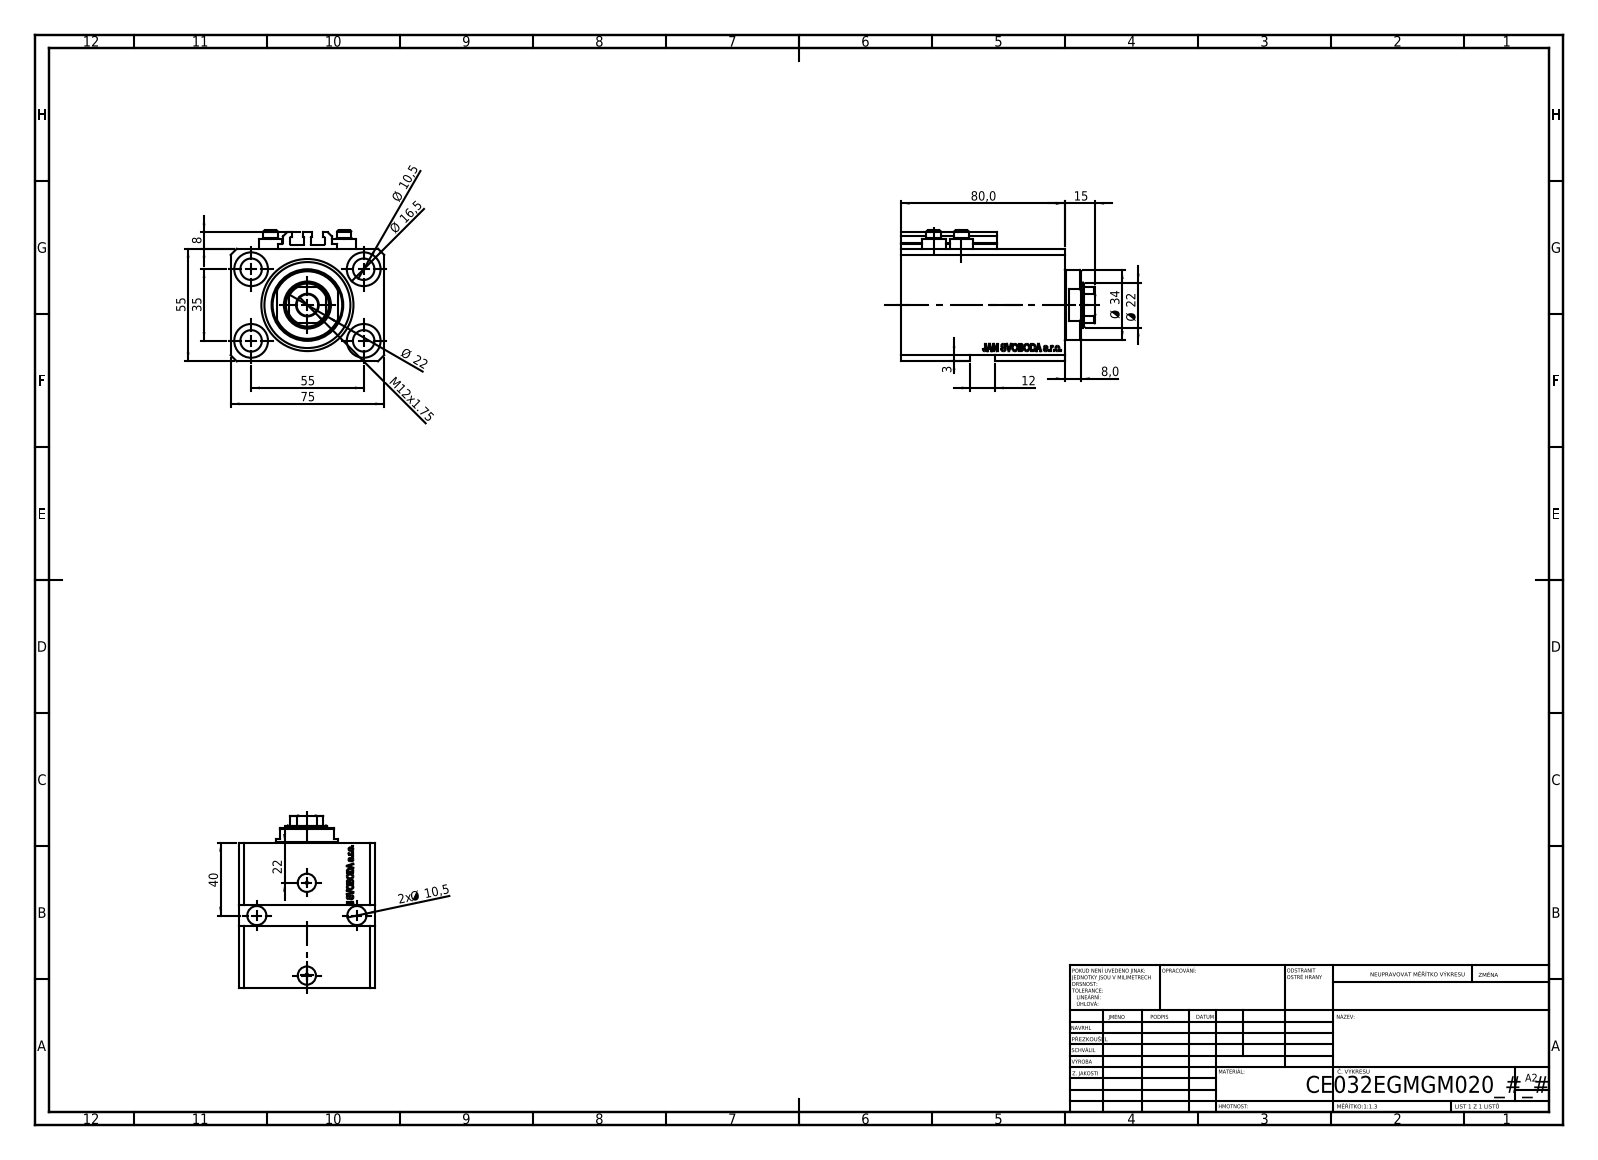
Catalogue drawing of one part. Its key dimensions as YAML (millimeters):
part_name: "V250CE_C_VCP; V250CE_VC_E; ALLEN BOLT V250CE; V250CE_E_Body"
step_written_by: "SolidWorks 2019 (CONFIG_CONTROL_DESIGN)"
units: millimeters
bodies: {solids: 8, faces: 1064, planar: 514, cylindrical: 126, other: 424}
overall_size: [95, 75, 64]
volume: 283894
surface_area: 74463
round_holes:
  - {diameter: 10.5, count: 7}
  - {diameter: 1.25, count: 4}
  - {diameter: 4, count: 4}
  - {diameter: 16.5, count: 4}
  - {diameter: 10, count: 2}
  - {diameter: 13.16, count: 2}
  - {diameter: 20, count: 2}
  - {diameter: 22, count: 1}
  - {diameter: 32, count: 1}
  - {diameter: 45, count: 1}
round_bosses_or_shafts:
  - {diameter: 11.6, count: 4}
  - {diameter: 7, count: 4}
  - {diameter: 34, count: 1}
partial_cylinders:
  - {radius: 0.2, count: 10}
  - {radius: 10.5, count: 1}
face_to_face_distances: [55, 75, 15, 80, 65, 3, 55.1, 9.9, 70.1, 54]
hole_center_spacings: [32.6, 55, 13.6, 14.09, 19.89, 20.12, 25.81, 28.48]
